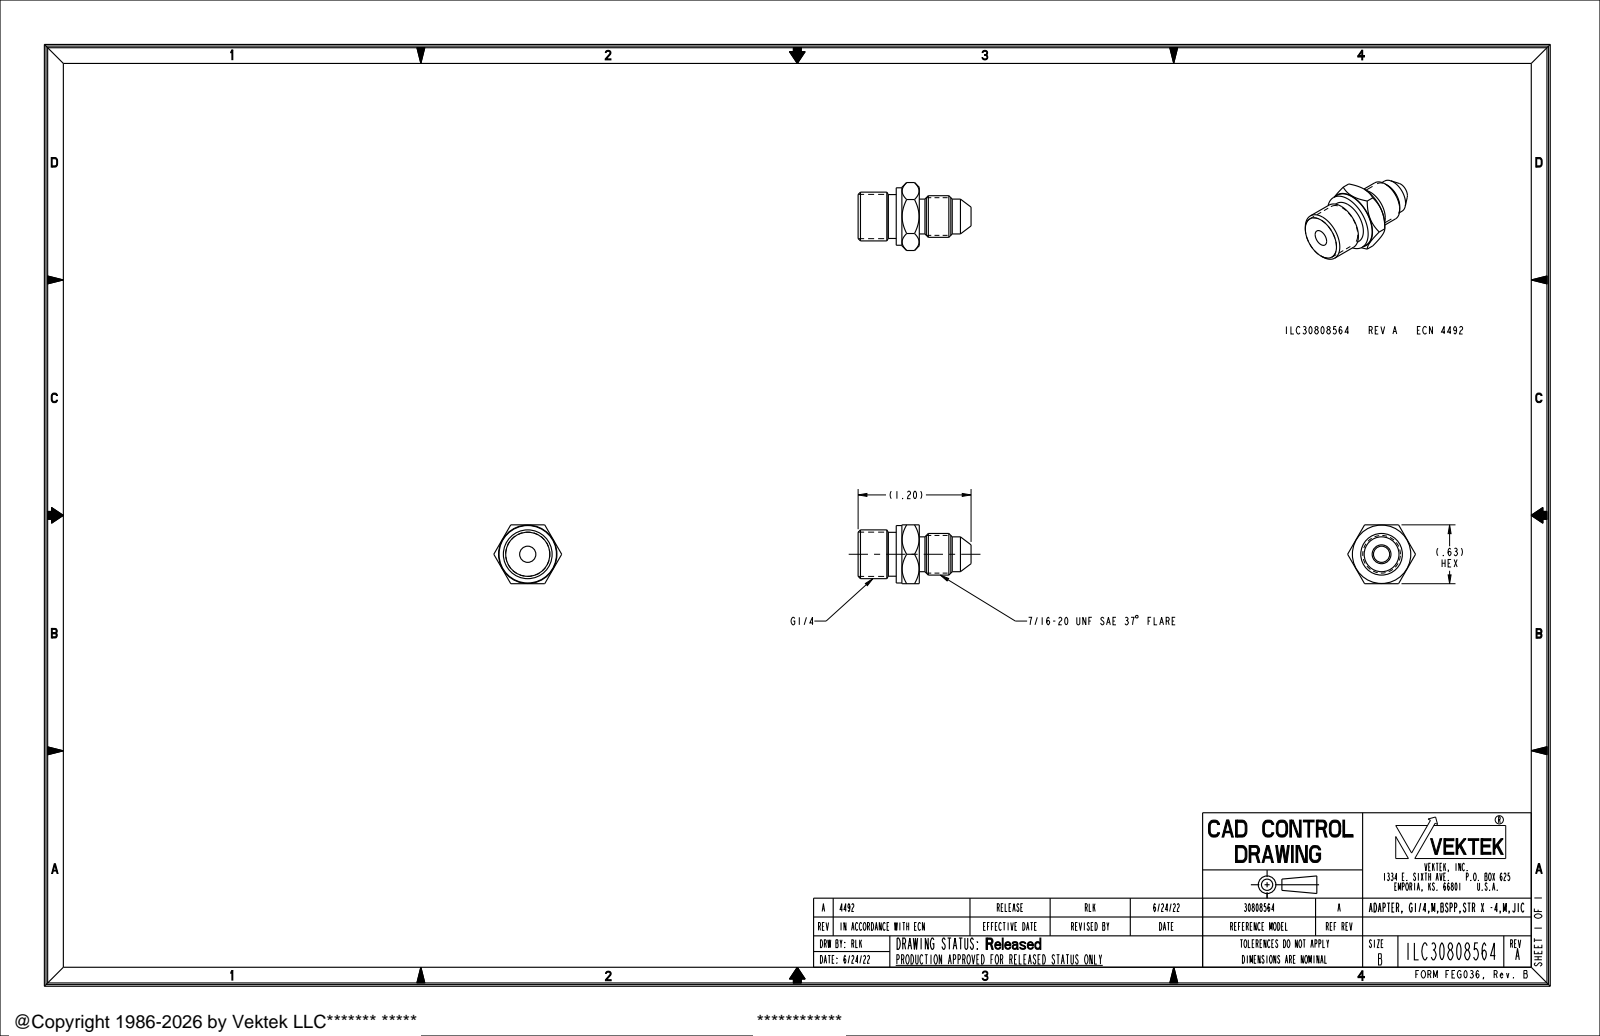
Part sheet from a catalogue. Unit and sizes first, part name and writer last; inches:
Units: inches
Overall size (bounding box): 1.2 × 0.722 × 0.625
Round holes (diameter × count): ⌀0.172 ×1
Round bosses / shafts (diameter × count): ⌀0.61 ×1, ⌀0.518 ×1, ⌀0.47 ×1, ⌀0.466 ×1, ⌀0.442 ×1, ⌀0.4 ×1, ⌀0.37 ×1
Main face-to-face distances: 0.625, 0.65, 0.245, 0.405, 0.185, 0.06, 0.465, 0.55, 0.735, 0.795
Volume: 0.198 in³ · Surface area: 3.876 in²
Bodies: 1 solid, 43 faces (11 planar, 18 cylindrical, 14 other)
Part name (STEP PRODUCT): ILC30808564
STEP written by: CREO PARAMETRIC BY PTC INC, 2021164 (AUTOMOTIVE_DESIGN)
